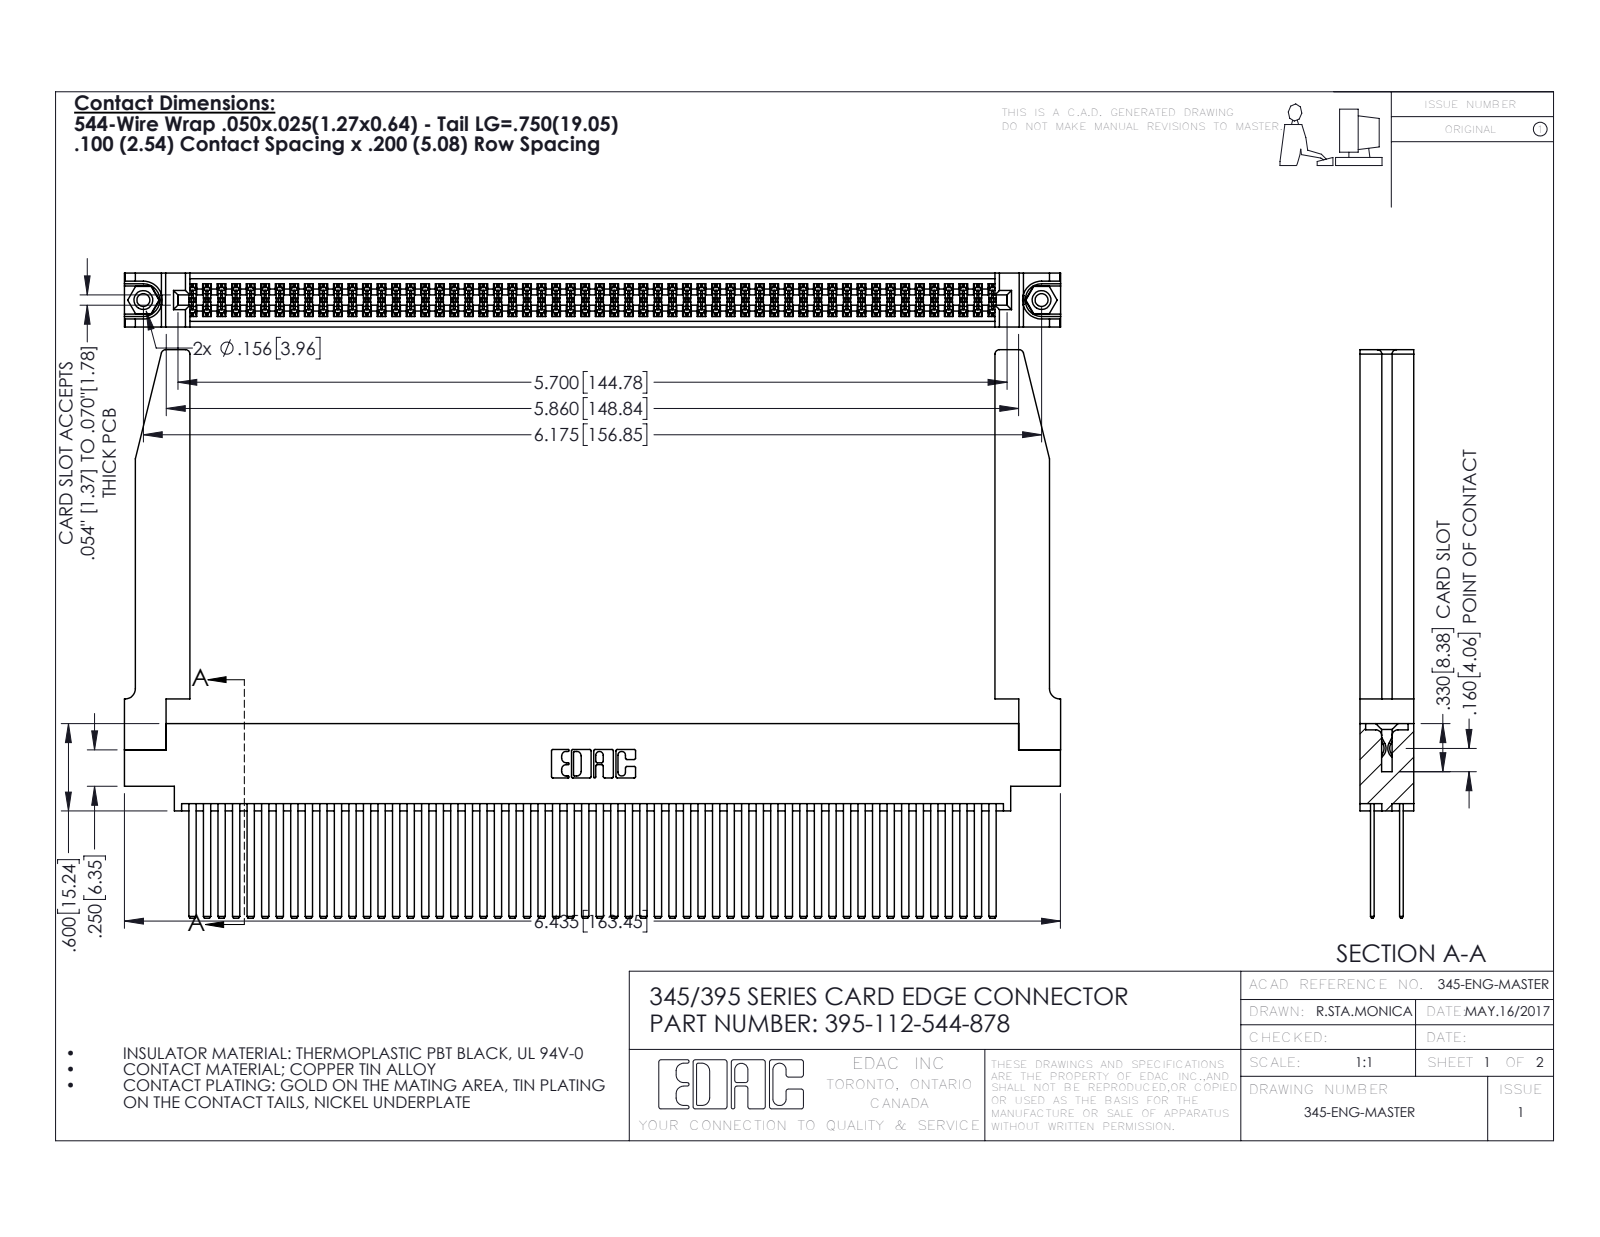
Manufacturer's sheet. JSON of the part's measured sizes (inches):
{"part_name": "345 Part_0.170 Offset - 0.156 Dia-TH; 345-220-078_345-220-078; 395-112-544-878; 345-250-001_345-250-001-102 (+1 more)", "step_written_by": "SolidWorks 2016 (CONFIG_CONTROL_DESIGN)", "units": "inches", "bodies": {"solids": 117, "faces": 5292, "planar": 3474, "cylindrical": 1766, "other": 52}, "overall_size": [6.436, 3.907, 0.37], "volume_in3": 1.54, "surface_area_in2": 58.39, "round_holes": [[0.089, 2], [0.125, 2], [0.156, 2], [0.064, 1]], "round_bosses_or_shafts": [[0.155, 2]], "partial_cylinders_radius": [[0.006, 168], [0.01, 22], [0.03, 8], [0.007, 6], [0.031, 6], [0.026, 3], [0.014, 2], [0.019, 2]], "face_to_face_distances": [0.072, 0.298, 0.098, 0.272, 0.025, 0.2, 0.37, 0.225, 0.175, 0.148], "hole_center_spacings": [0.27, 5.939, 6.175]}
